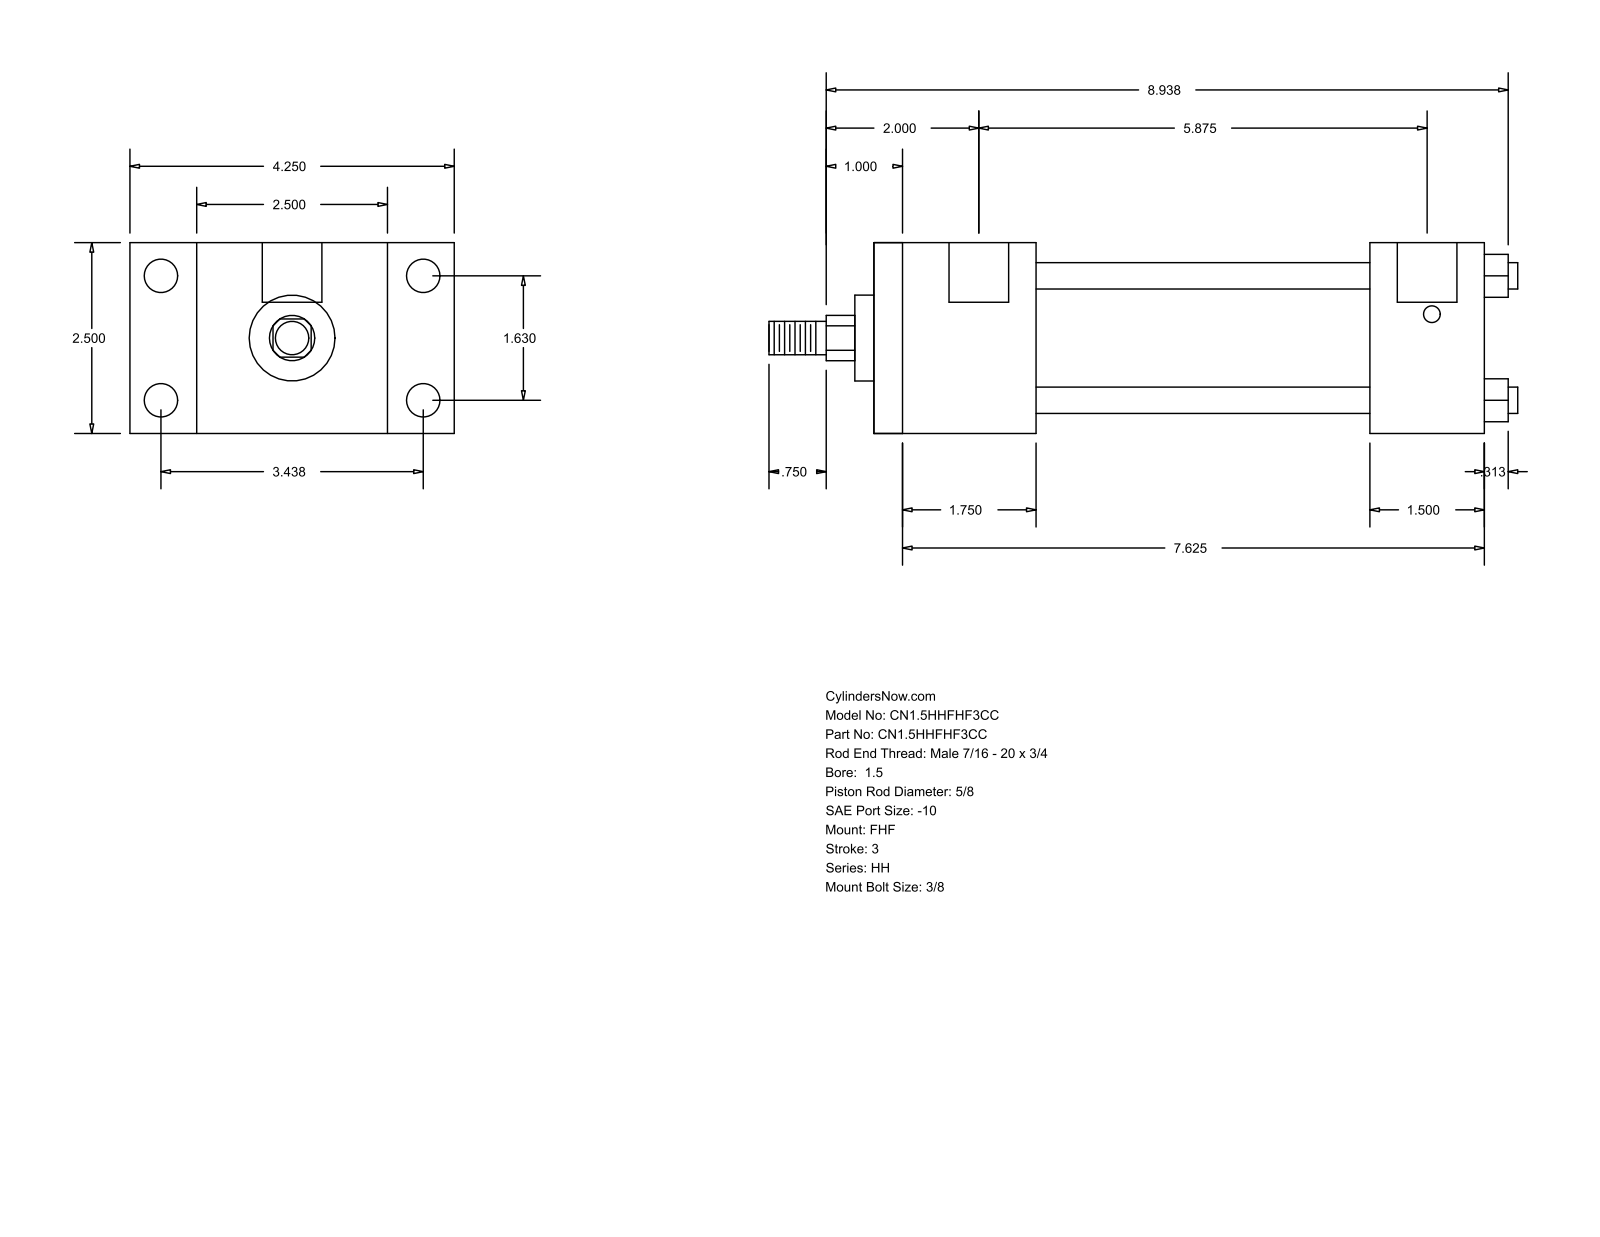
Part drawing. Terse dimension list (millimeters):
name: HH_FHF__0150_0.625
written by: GSSL Pune (CONFIG_CONTROL_DESIGN)
unit: mm
bodies: 0 solids, 88 faces (60 planar, 28 cylindrical, 0 other)
size: 249.24 × 107.95 × 63.5
holes: 4× ⌀5.56, 4× ⌀11.13, 2× ⌀19.84
bosses: 4× ⌀8.76, 1× ⌀44.45, 1× ⌀28.57, 1× ⌀15.88, 1× ⌀11.11
rounds: 1× R7.54
face distances: 63.5, 22.23, 85.73, 53.97, 107.96, 203.19, 149.22, 38.1, 165.09, 111.12
hole spacings: 41.4, 87.32, 96.64, 152.4, 1.58, 1.59, 149.23, 150.81
